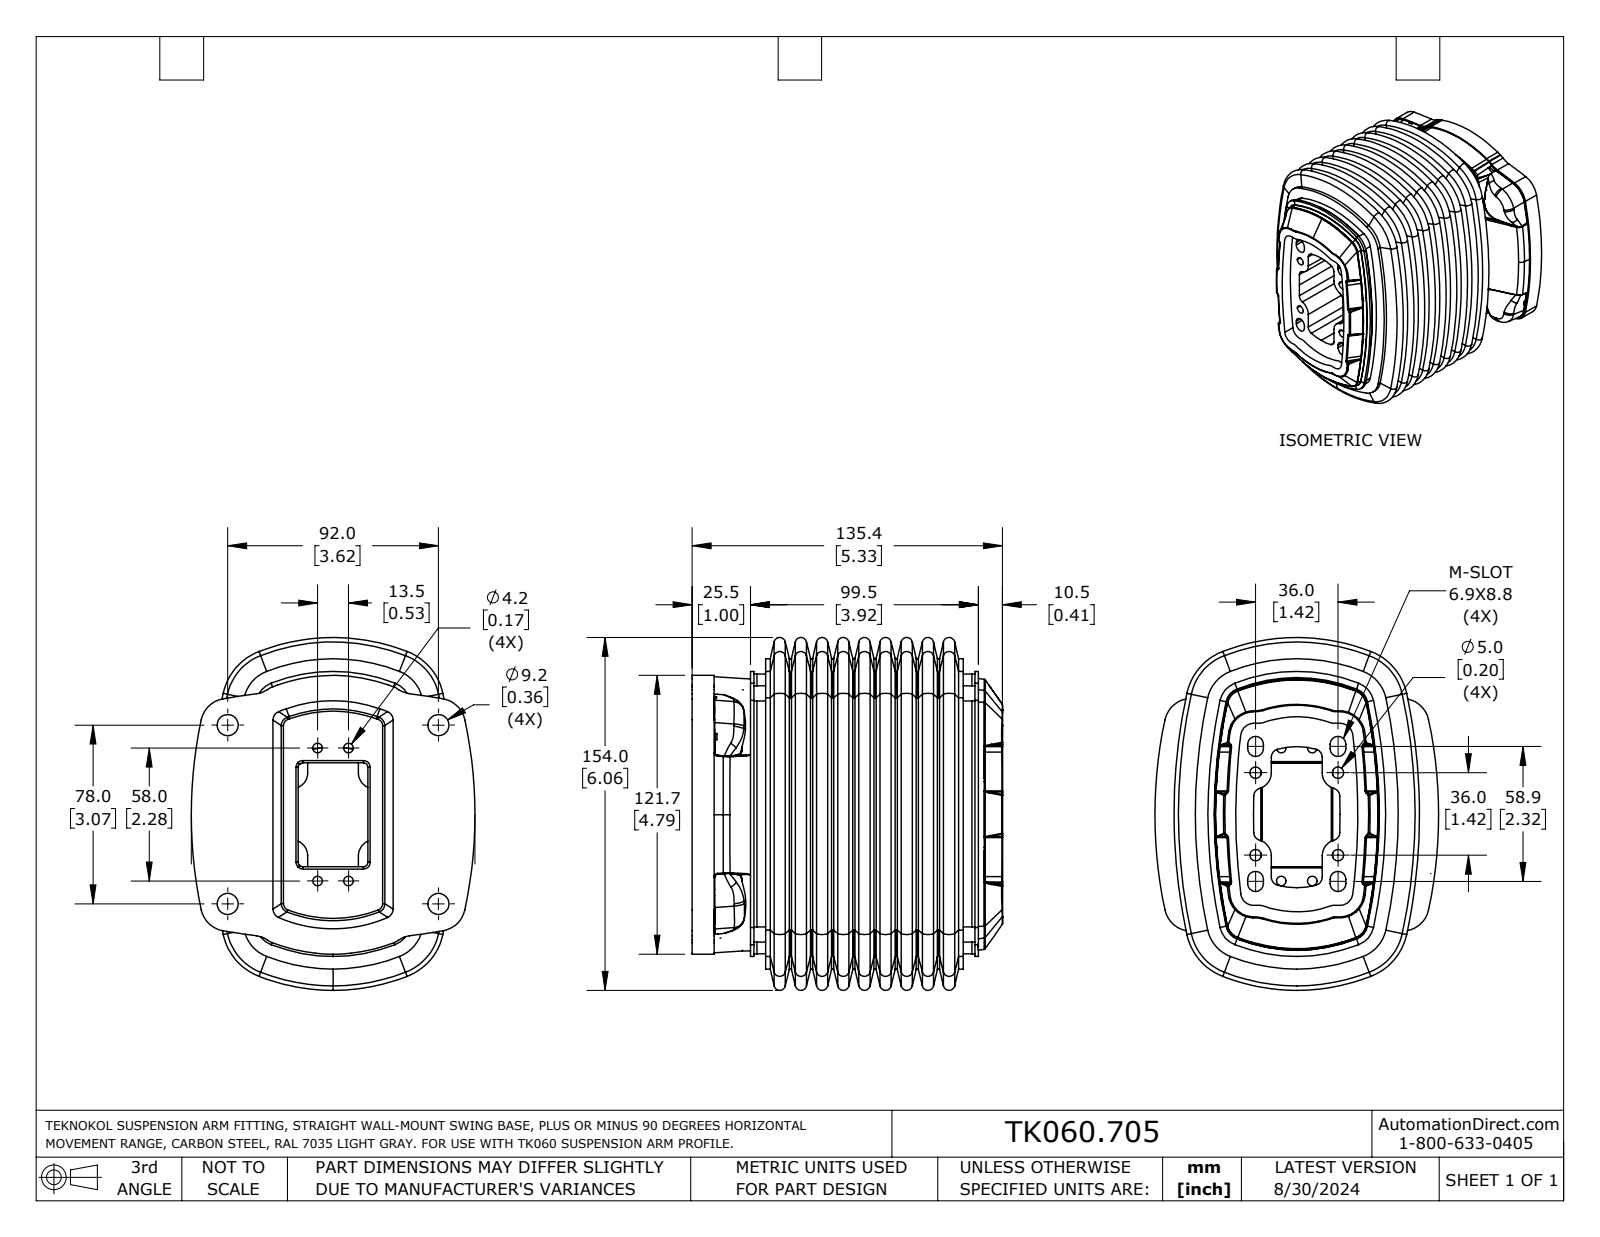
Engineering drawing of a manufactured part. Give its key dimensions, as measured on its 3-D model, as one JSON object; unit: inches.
{"part_name": "TK060.705_REV4", "step_written_by": "SolidWorks 2023 (AUTOMOTIVE_DESIGN)", "units": "inches", "bodies": {"solids": 1, "faces": 785, "planar": 61, "cylindrical": 76, "other": 648}, "overall_size": [6.049, 5.338, 4.876], "volume_in3": 76.96, "surface_area_in2": 245.6, "round_holes": [[0.197, 4], [0.362, 4]], "partial_cylinders_radius": [[0.028, 8], [0.136, 8], [0.144, 4], [0.147, 4], [0.354, 4], [0.361, 4], [0.625, 4], [2.324, 4]], "face_to_face_distances": [0.593, 1.473, 0.834, 0.428, 1.262, 3.399, 3.827, 4.661, 0.401, 3.8], "hole_center_spacings": [1.384, 2.497, 2.654, 3.371, 1.404, 1.417, 1.994, 3.077]}
